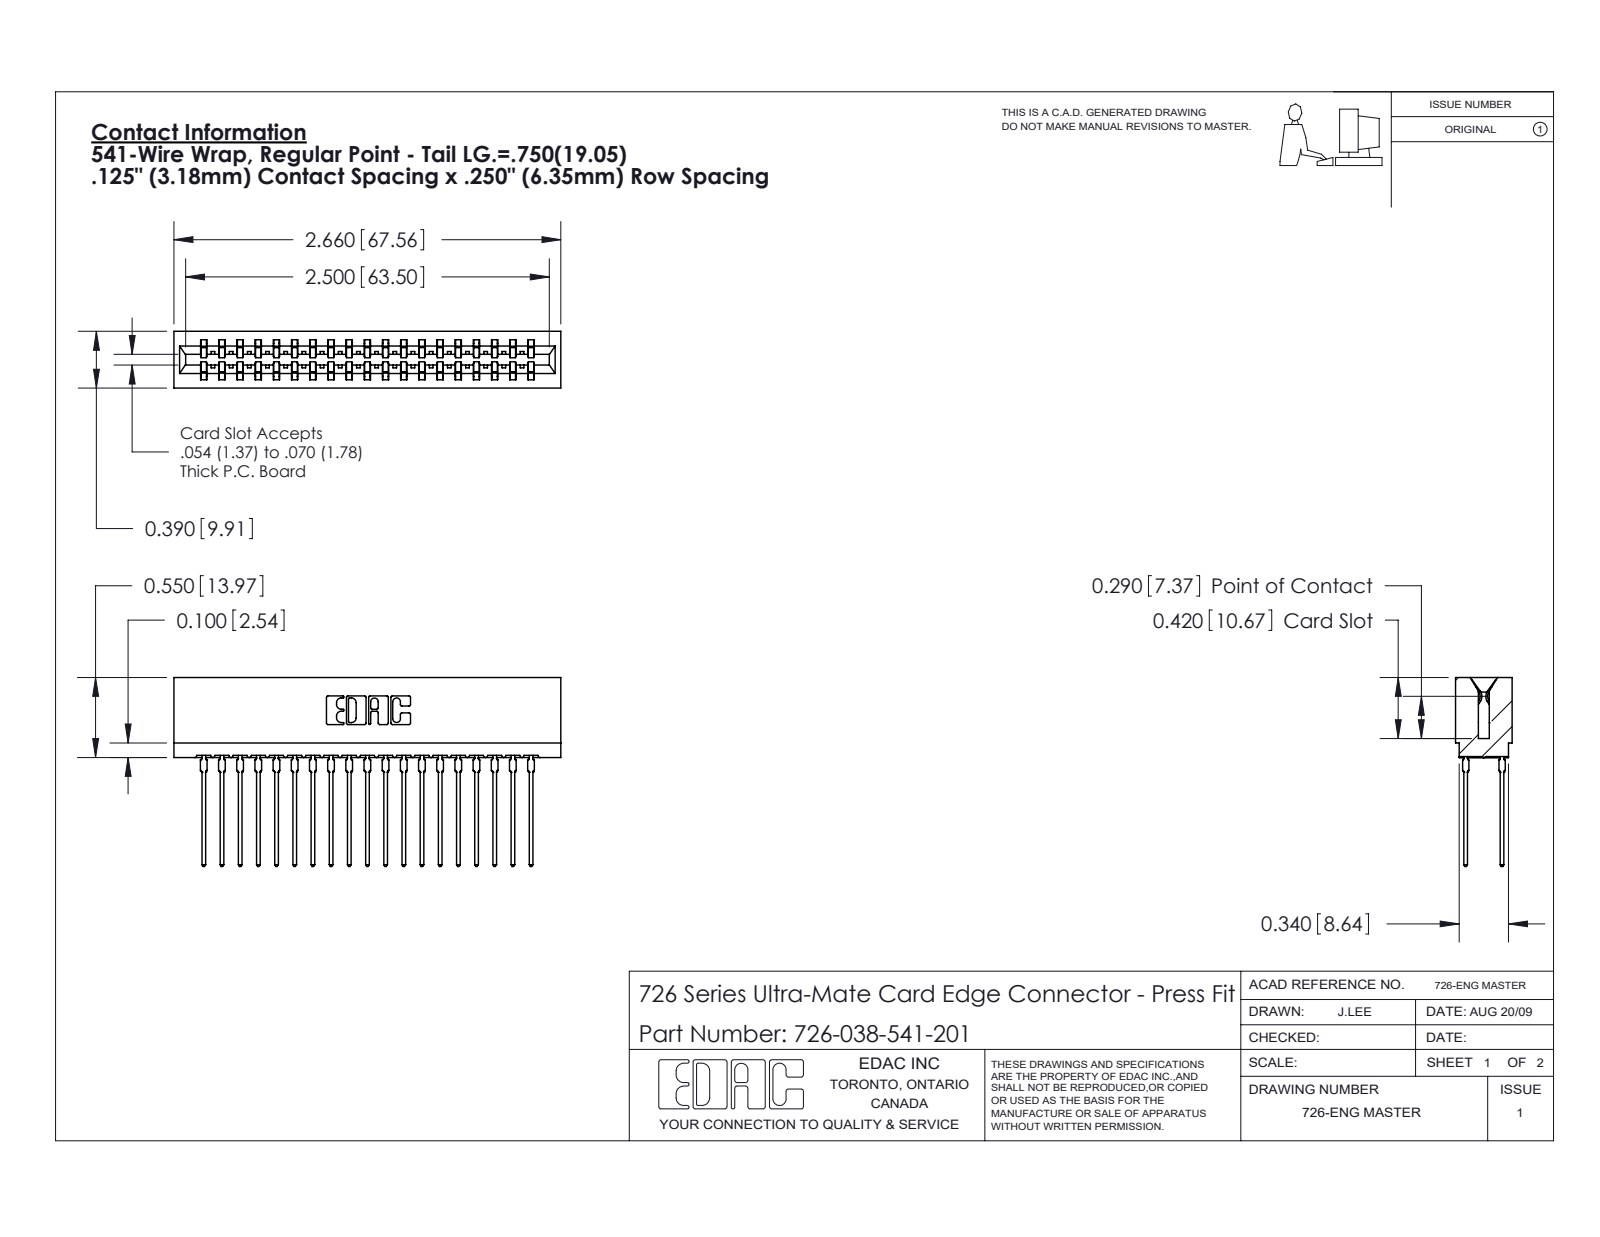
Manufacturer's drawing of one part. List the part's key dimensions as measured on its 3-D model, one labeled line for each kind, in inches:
Part name (STEP PRODUCT): 746-292-001_541; 726 Part_.515 Slot Depth - 01; 726-038-541-201
STEP written by: SolidWorks 2020 (CONFIG_CONTROL_DESIGN)
Units: inches
Bodies: 39 solids, 3498 faces (1803 planar, 707 cylindrical, 988 other)
Overall size (bounding box): 2.66 × 1.299 × 0.39
Volume: 0.399 in³ · Surface area: 17.78 in²
Partial cylindrical surfaces — rounded edges, fillets, slot ends (radius × count): R0.021 ×76, R0.01 ×22, R0.015 ×20, R0.005 ×8, R0.011 ×8, R0.007 ×6, R0.031 ×6, R0.026 ×3
Main face-to-face distances: 0.057, 0.333, 0.25, 0.025, 0.307, 0.39, 0.083, 0.5, 0.275, 0.125
